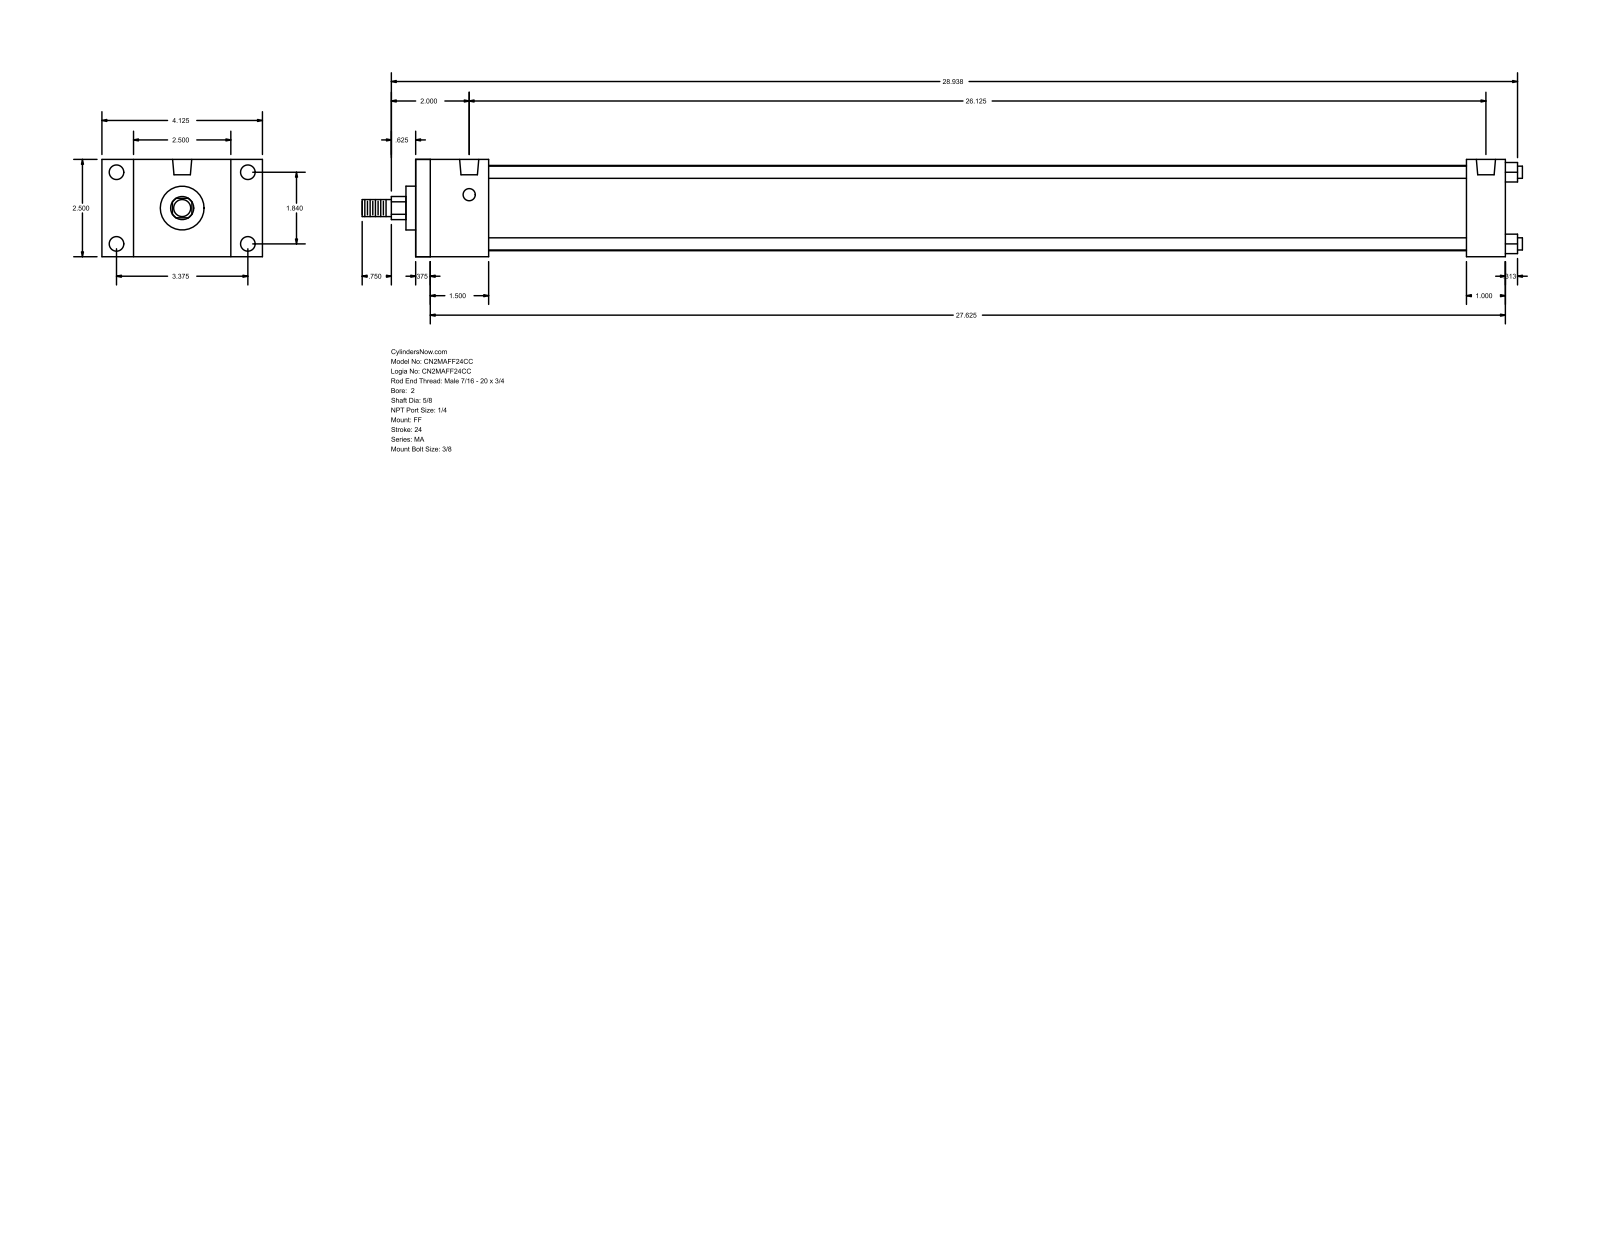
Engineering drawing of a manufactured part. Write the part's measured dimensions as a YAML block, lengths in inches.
part_name: "MA_FF__0200_0.625"
step_written_by: "GSSL Pune (CONFIG_CONTROL_DESIGN)"
units: inches
bodies: {solids: 0, faces: 92, planar: 64, cylindrical: 28, other: 0}
overall_size: [29.813, 4.125, 2.5]
round_holes:
  - {diameter: 0.313, count: 4}
  - {diameter: 0.375, count: 4}
  - {diameter: 0.492, count: 2}
round_bosses_or_shafts:
  - {diameter: 0.313, count: 4}
  - {diameter: 2.19, count: 1}
  - {diameter: 1.125, count: 1}
  - {diameter: 0.625, count: 1}
  - {diameter: 0.437, count: 1}
partial_cylinders:
  - {radius: 0.297, count: 1}
face_to_face_distances: [2.5, 28, 0.375, 27.625, 1.5, 1.875, 27, 26.625, 25.125, 26.125]
hole_center_spacings: [1.84, 3.375, 3.844, 26.125]
